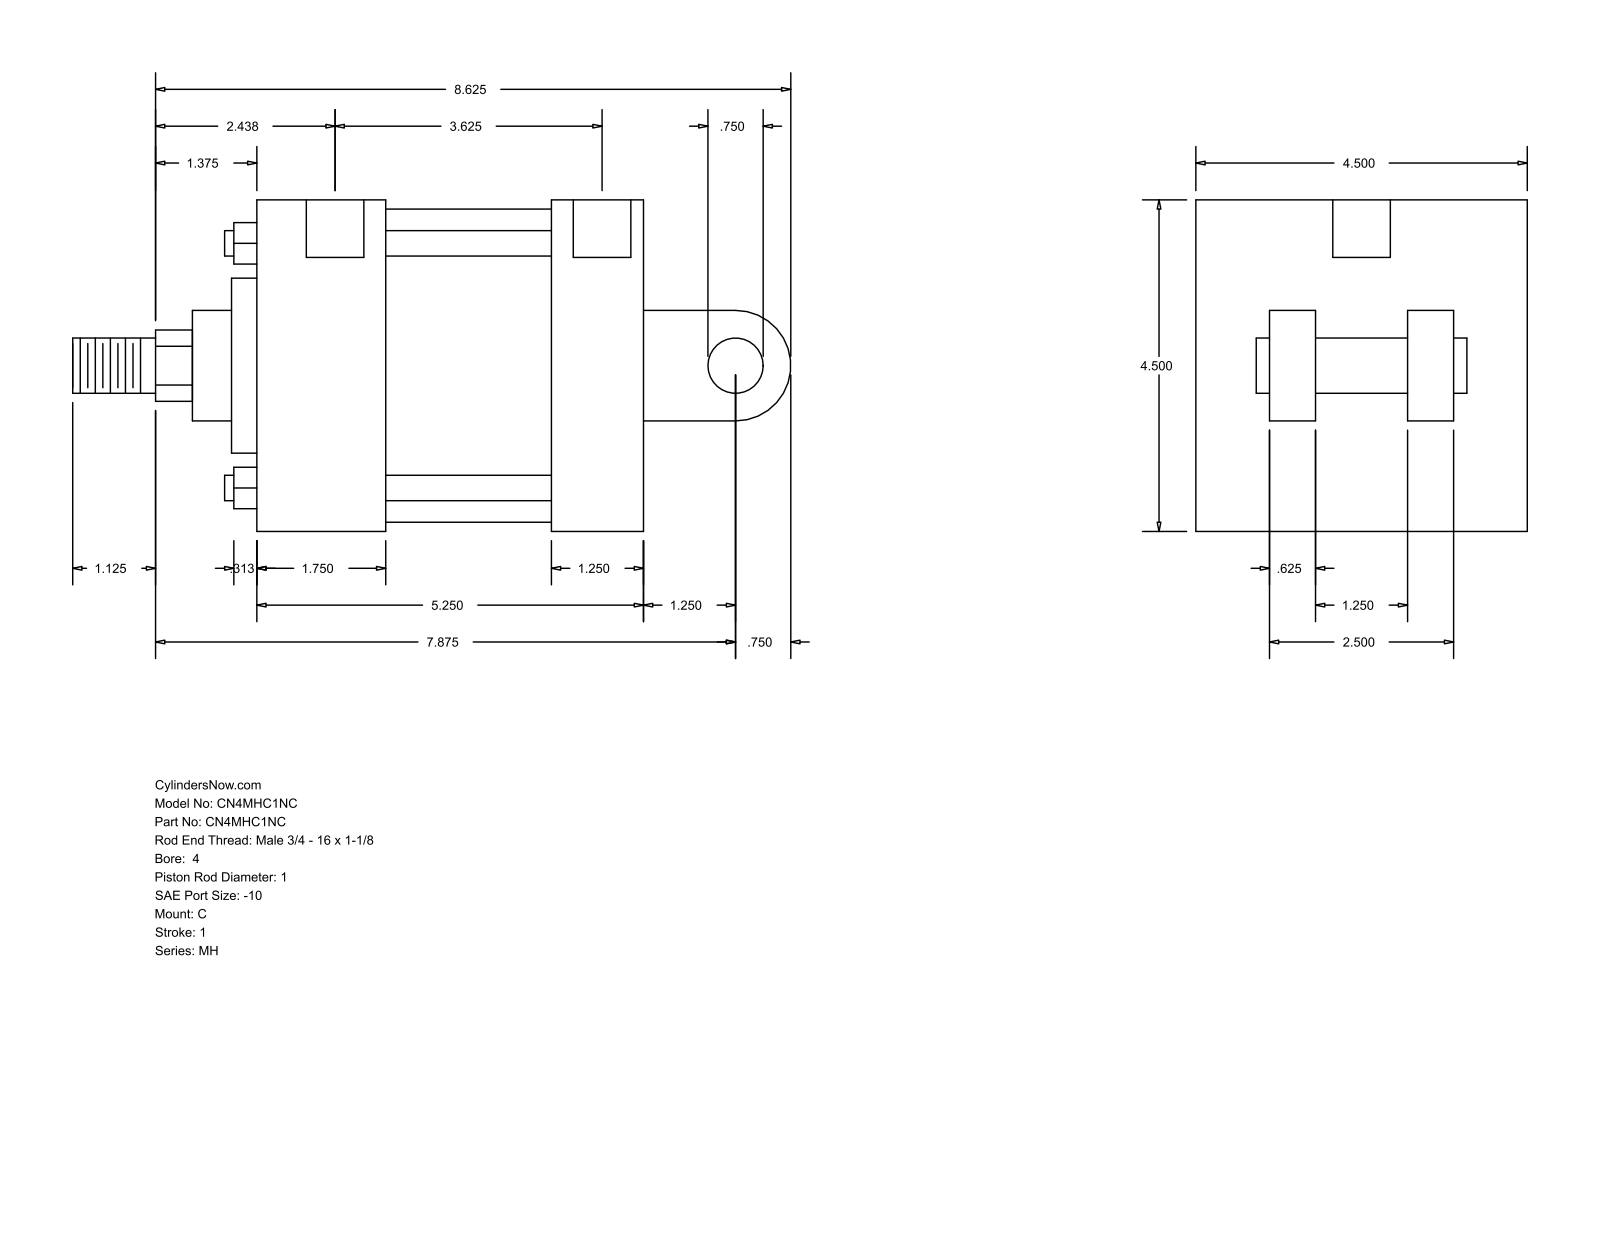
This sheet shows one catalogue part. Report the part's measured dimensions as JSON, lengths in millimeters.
{"part_name": "MH_C__0400_1", "step_written_by": "GSSL Pune (CONFIG_CONTROL_DESIGN)", "units": "millimeters", "bodies": {"solids": 0, "faces": 101, "planar": 71, "cylindrical": 30, "other": 0}, "overall_size": [247.65, 114.3, 114.3], "round_holes": [[8.73, 4], [19.84, 2]], "round_bosses_or_shafts": [[8.76, 4], [19.05, 2], [107.95, 1], [60.33, 1], [38.1, 1], [25.4, 1]], "partial_cylinders_radius": [[12.29, 1], [19.05, 1]], "face_to_face_distances": [114.3, 133.36, 88.9, 44.46, 101.61, 57.15, 31.75, 73.03, 41.27, 38.1], "hole_center_spacings": [1.58, 93.66, 95.24, 92.08]}
